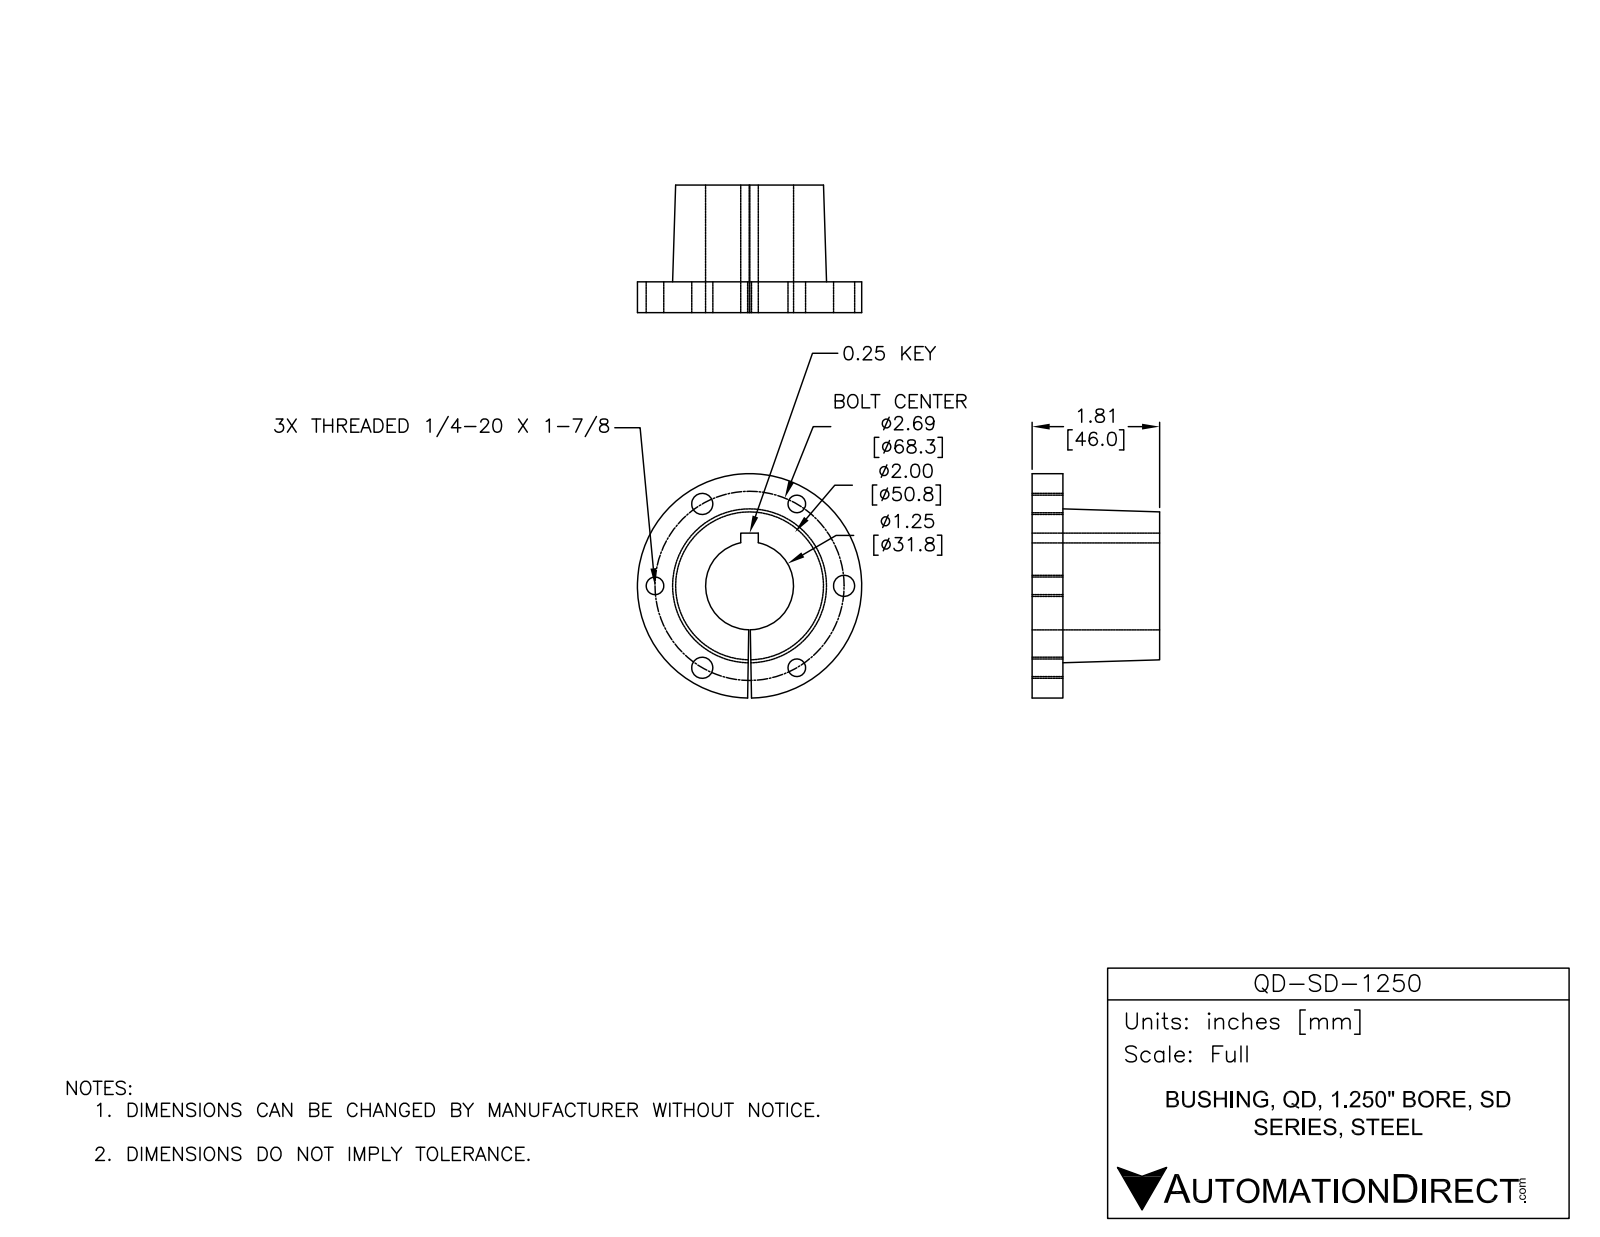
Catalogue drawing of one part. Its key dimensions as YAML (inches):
part_name: "QD-SD-1250"
step_written_by: "SolidWorks 2014 (AUTOMOTIVE_DESIGN)"
units: inches
bodies: {solids: 1, faces: 29, planar: 8, cylindrical: 18, other: 3}
overall_size: [3.188, 3.187, 1.813]
volume: 5.991
surface_area: 37.8
round_holes:
  - {diameter: 0.25, count: 3}
  - {diameter: 0.3, count: 3}
  - {diameter: 1.25, count: 1}
round_bosses_or_shafts:
  - {diameter: 3.187, count: 1}
face_to_face_distances: [0.437, 1.812, 1.375, 0.25]
hole_center_spacings: [1.344, 2.328, 1.344, 2.688, 2.687]
